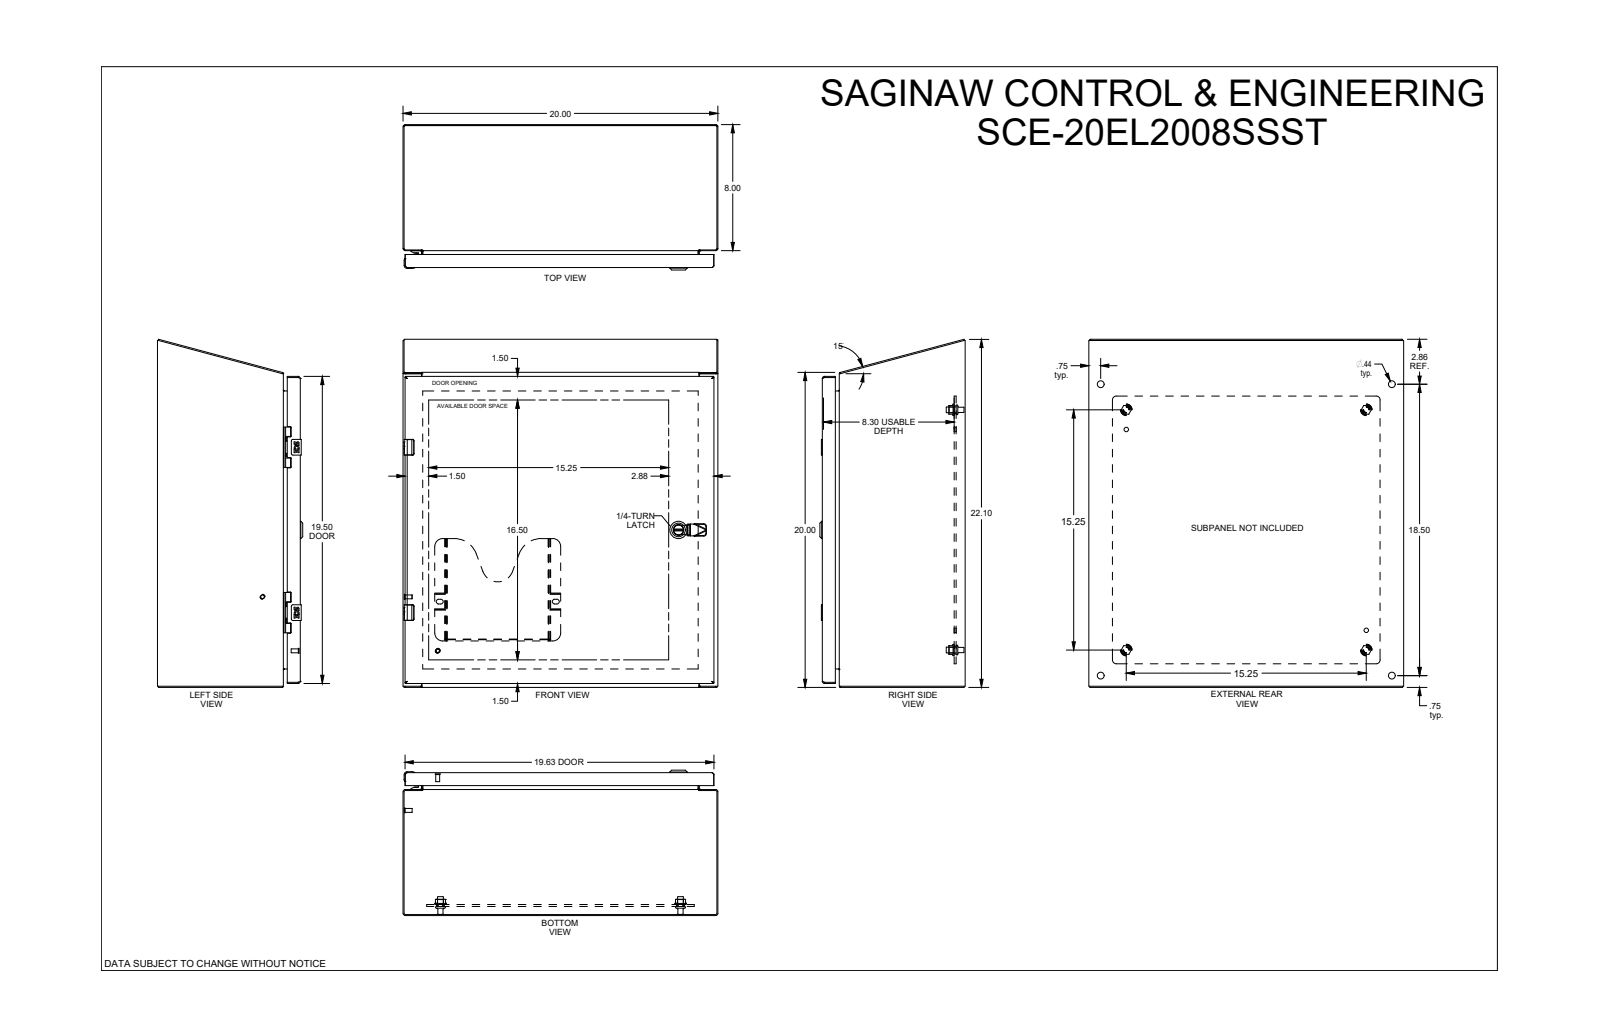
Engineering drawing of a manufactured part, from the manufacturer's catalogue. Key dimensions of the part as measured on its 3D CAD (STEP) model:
Part name (STEP PRODUCT): SCE-20EL2008SSST_REV1
STEP written by: SolidWorks 2021 (AUTOMOTIVE_DESIGN)
Units: inches
Bodies: 26 solids, 1333 faces (619 planar, 485 cylindrical, 229 other)
Overall size (bounding box): 22.106 × 20 × 9.935
Volume: 173.7 in³ · Surface area: 4 240 in²
Round holes (diameter × count): ⌀0.172 ×4, ⌀0.205 ×4, ⌀0.244 ×4, ⌀0.266 ×4, ⌀0.437 ×4, ⌀0.5 ×4, ⌀0.187 ×2, ⌀0.218 ×2, ⌀0.281 ×2, ⌀0.375 ×2, ⌀0.375 ×2, ⌀0.193 ×1
Round bosses / shafts (diameter × count): ⌀0.375 ×4, ⌀0.33 ×4, ⌀0.25 ×4, ⌀0.248 ×4, ⌀1.102 ×1, ⌀0.78 ×1, ⌀0.63 ×1, ⌀0.504 ×1
Partial cylindrical surfaces — rounded edges, fillets, slot ends (radius × count): R0.015 ×28, R0.04 ×23, R0.22 ×16, R0.06 ×15, R0.07 ×10, R0.145 ×10, R0.03 ×8, R0.031 ×8
Main face-to-face distances: 0.075, 0.075, 0.06, 9.068, 8.993, 9.008, 8.933, 19.925, 0.125, 0.5
Hole centre spacings: 16.953, 10.5, 0.985, 16.927, 17.065, 18.5, 18.986, 23.771
